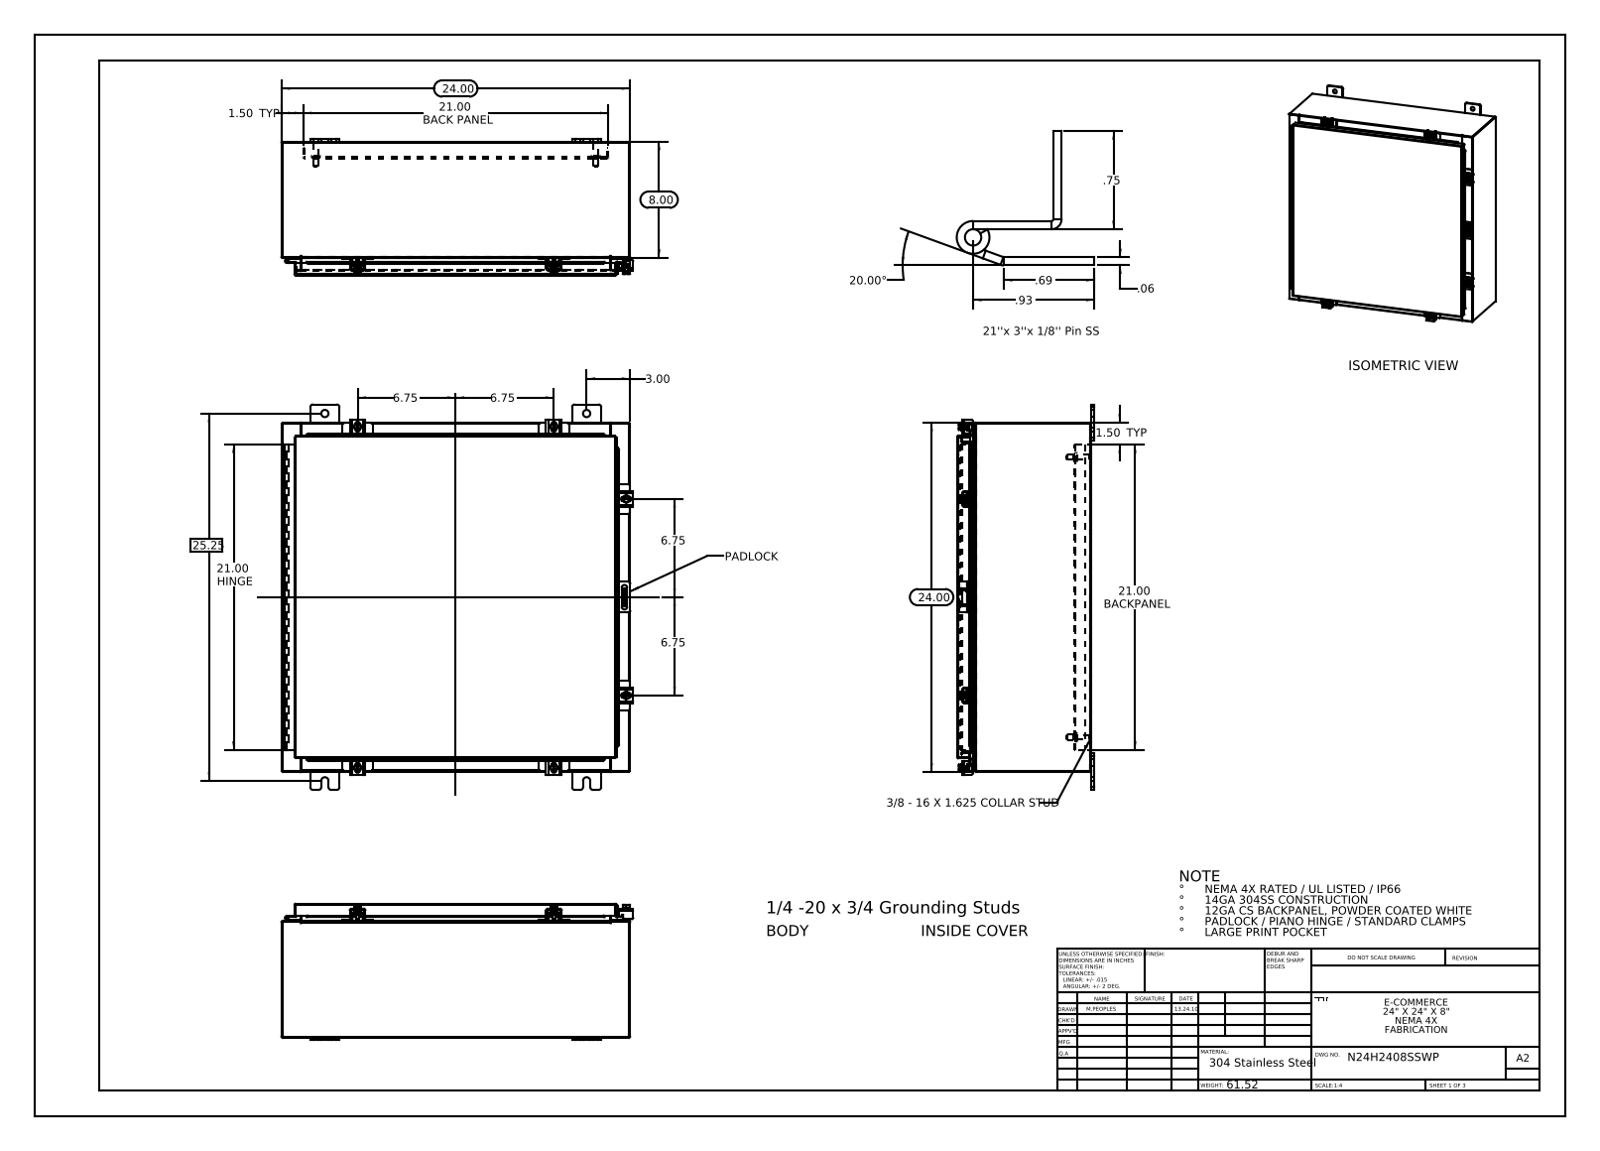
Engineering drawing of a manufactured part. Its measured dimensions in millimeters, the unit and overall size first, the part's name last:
Units: millimetres
Overall size (bounding box): 673.1 × 615 × 238.5
Round holes (diameter × count): ⌀12.7 ×8, ⌀5.4 ×6, ⌀6.6 ×6, ⌀3.2 ×2, ⌀3.2 ×1
Round bosses / shafts (diameter × count): ⌀6.4 ×7, ⌀12.7 ×6, ⌀10.1 ×6, ⌀15.9 ×4, ⌀9.5 ×4, ⌀8.4 ×4
Partial cylindrical surfaces — rounded edges, fillets, slot ends (radius × count): R1.5 ×30, R0.3 ×25, R4.8 ×24, R2.2 ×21, R3 ×12, R3.6 ×12, R3.2 ×10, R1.3 ×9
Main face-to-face distances: 1.9, 231.8, 607.7, 233.7, 229.9, 2.6, 25.4, 27.3, 204.5, 206.4
Hole centre spacings: 419.3, 486, 547.2, 683.4, 342.9, 47.2, 57.8, 61.5
Volume: 3 543 000 mm³ · Surface area: 3 504 000 mm²
Bodies: 47 solids, 1709 faces (908 planar, 705 cylindrical, 96 other)
Part name (STEP PRODUCT): N24H2408SSWP Standard Clamps; N24H2408SSWP Clamp Top; N24H2408SSWP Body; N24H2408SSWP 125 Pin Hinge (+8 more)
STEP written by: SolidWorks 2013 (CONFIG_CONTROL_DESIGN)
